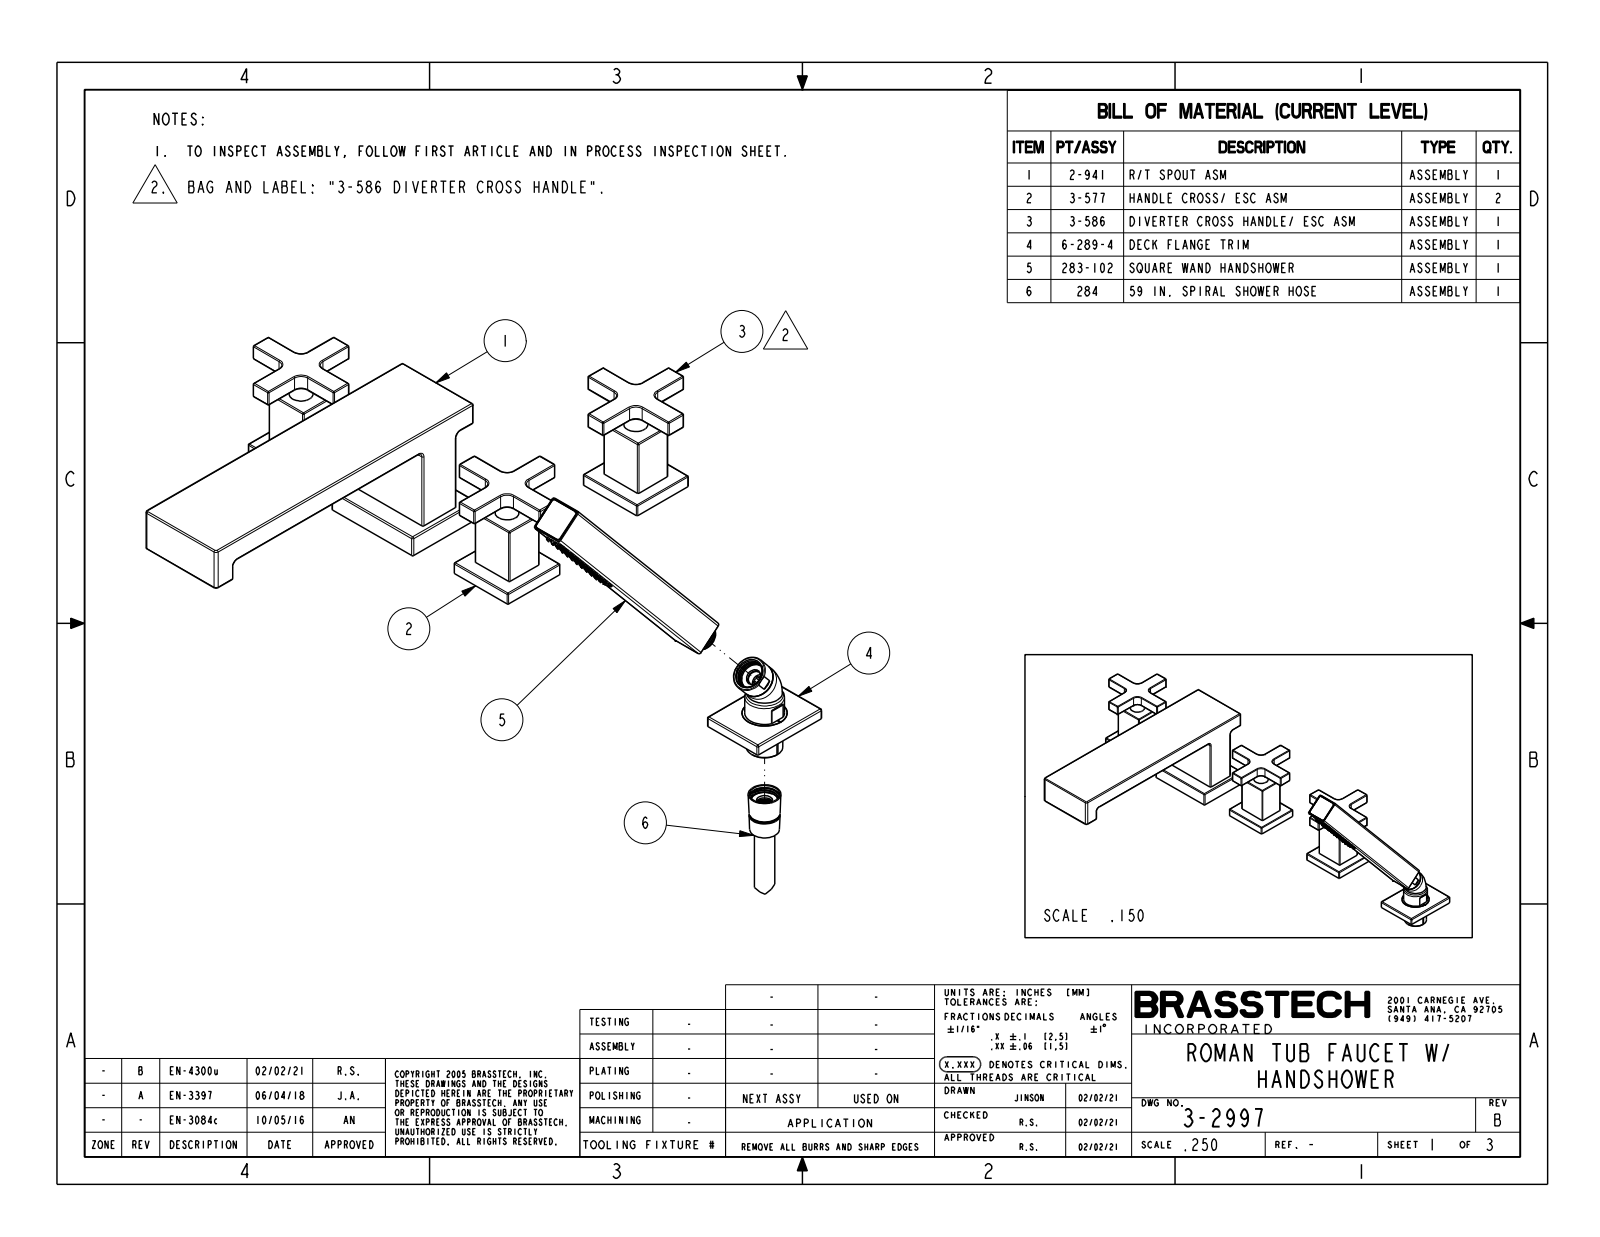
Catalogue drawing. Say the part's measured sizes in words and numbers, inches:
The part is named "3-2997". Its 3-D file was written by "CREO PARAMETRIC BY PTC INC, 2018400 (CONFIG_CONTROL_DESIGN)". It is 5 solids with 1215 faces: 171 planar, 378 cylindrical and 666 other. Overall it measures 20.555 by 10.251 by 8.772 inches. Its volume is 62.19 cubic inches and its surface area 261.6 square inches. Round holes: 44 of diameter 0.14, 1 of diameter 0.835. Round bosses or shafts: 3 of diameter 0.65, 3 of diameter 0.523, 1 of diameter 1.095, 1 of diameter 0.98, 1 of diameter 0.975, 1 of diameter 0.825. Partial cylindrical surfaces (rounded edges, fillets, slot ends): 98 of radius 0.03, 35 of radius 0.04, 16 of radius 0.01, 12 of radius 0.25, 6 of radius 0.05, 4 of radius 0.065, 3 of radius 0.16, 2 of radius 0.08. The main face-to-face distances are 3.76, 3.09, 0.67, 0.35, 0.07, 1.23, 3.046, 0.044, 0.714, 2.76. The hole center spacings are 0.336, 0.17, 0.447, 0.672, 0.604, 0.29, 0.87, 0.887.
